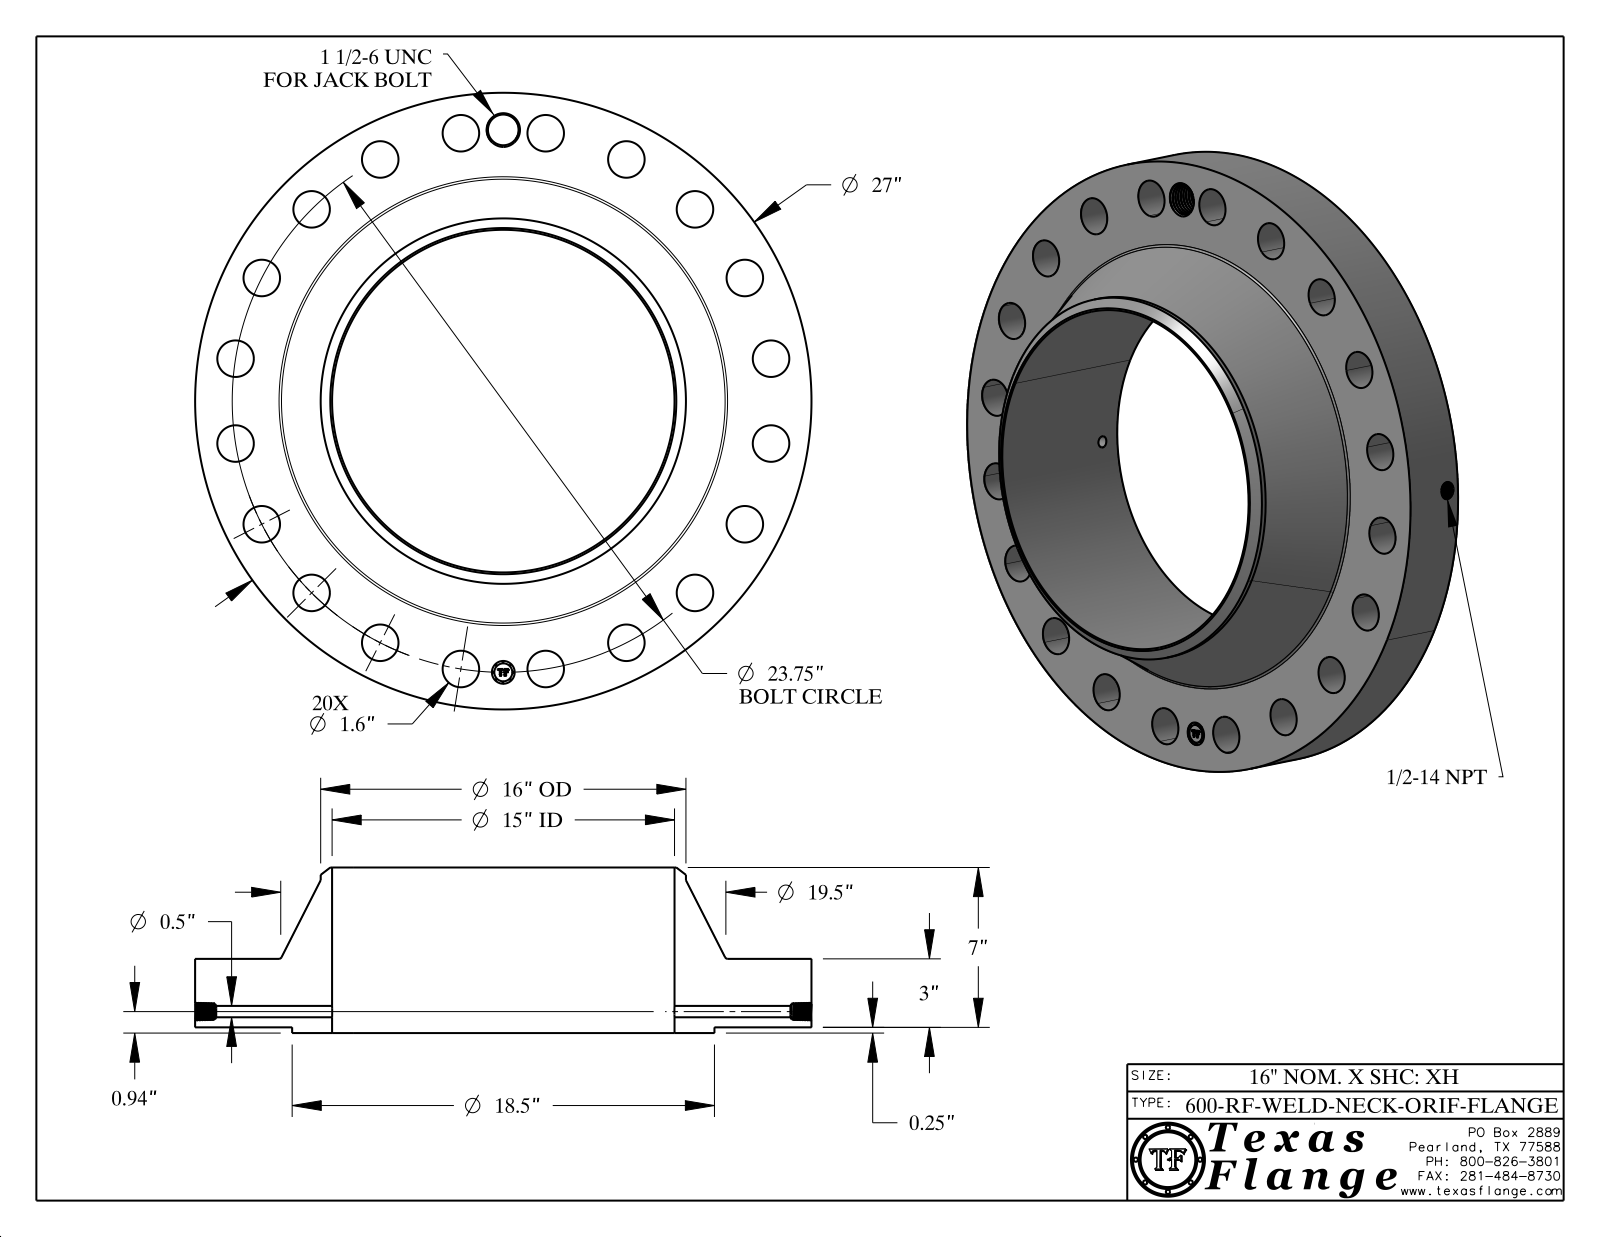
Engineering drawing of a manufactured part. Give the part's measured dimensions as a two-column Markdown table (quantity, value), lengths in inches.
| quantity | value |
| --- | --- |
| part name | 600-RF-WELD-NECK |
| STEP written by | CATIA V5 STEP AP214 (AUTOMOTIVE_DESIGN) |
| units | inches |
| bodies | 1 solid, 811 faces (369 planar, 124 cylindrical, 318 other) |
| overall size | 27 × 27 × 7.25 |
| volume | 1 339 in³ |
| surface area | 1 795 in² |
| round holes (diameter × count) | 1.6 × 20, 0.5 × 1, 0.672 × 1, 1 × 1, 1.344 × 1, 15 × 1 |
| round bosses / shafts (diameter × count) | 0.061 × 8, 27 × 1, 18.5 × 1, 16 × 1, 0.788 × 1 |
| main face-to-face distances | 3, 0.25, 3.25, 7.25, 7, 4, 0.015, 3.235, 2.985, 4.015 |
| hole center spacings | 11.875, 16.794, 22.587, 23.457, 3.715, 13.96, 19.214, 7.339 |
